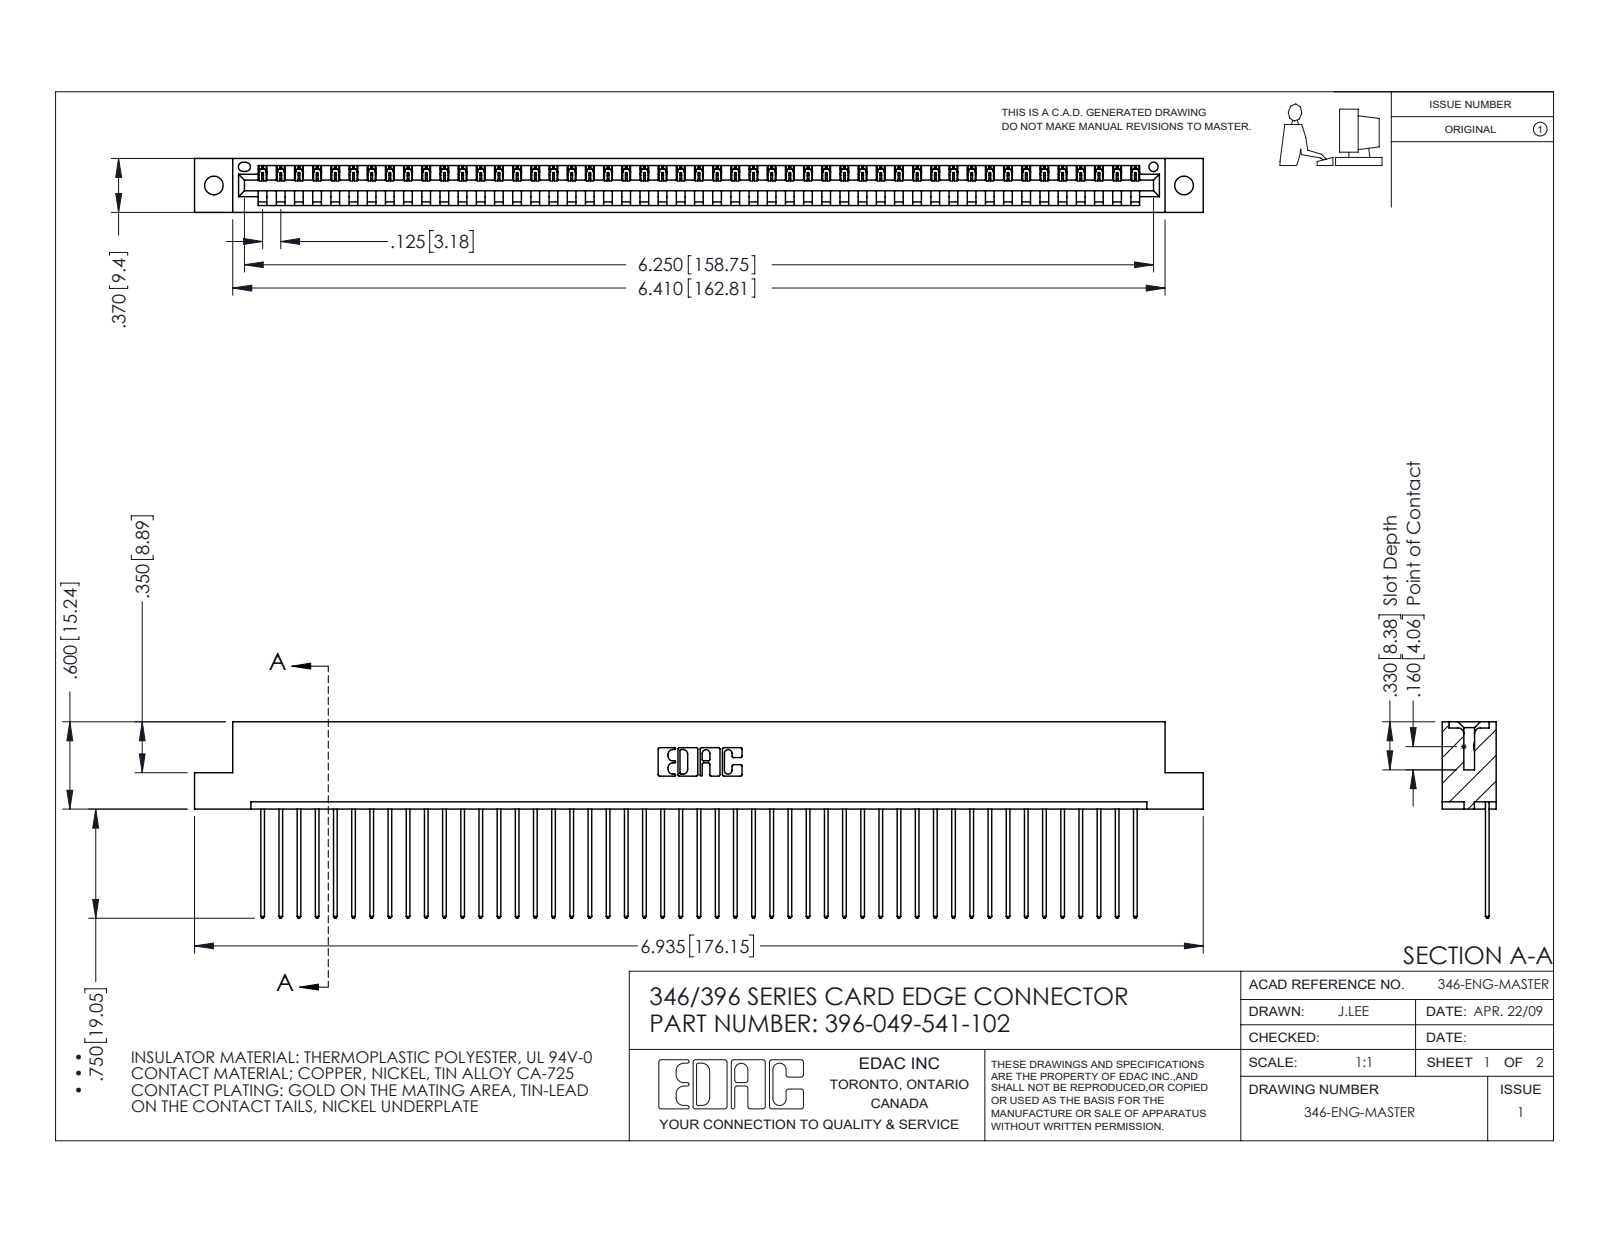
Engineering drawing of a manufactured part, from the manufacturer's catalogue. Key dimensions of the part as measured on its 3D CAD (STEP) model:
Part name (STEP PRODUCT): 345-292-001_345-293-141; 396-049-541-102; 346 Part_Flush Mounting Lugs - 0.128 Dia
STEP written by: SolidWorks 2016 (CONFIG_CONTROL_DESIGN)
Units: inches
Bodies: 50 solids, 2964 faces (2036 planar, 928 cylindrical, 0 other)
Overall size (bounding box): 6.935 × 1.35 × 0.37
Volume: 1.04 in³ · Surface area: 34.2 in²
Round holes (diameter × count): ⌀0.128 ×2, ⌀0.064 ×1
Partial cylindrical surfaces — rounded edges, fillets, slot ends (radius × count): R0.006 ×98, R0.01 ×98, R0.01 ×22, R0.007 ×6, R0.031 ×6, R0.026 ×3, R0.031 ×2, R0.04 ×2
Main face-to-face distances: 0.048, 0.322, 0.37, 0.25, 0.072, 0.298, 0.025, 0.148, 0.222, 0.1
Hole centre spacings: 0.246, 6.461, 6.67
